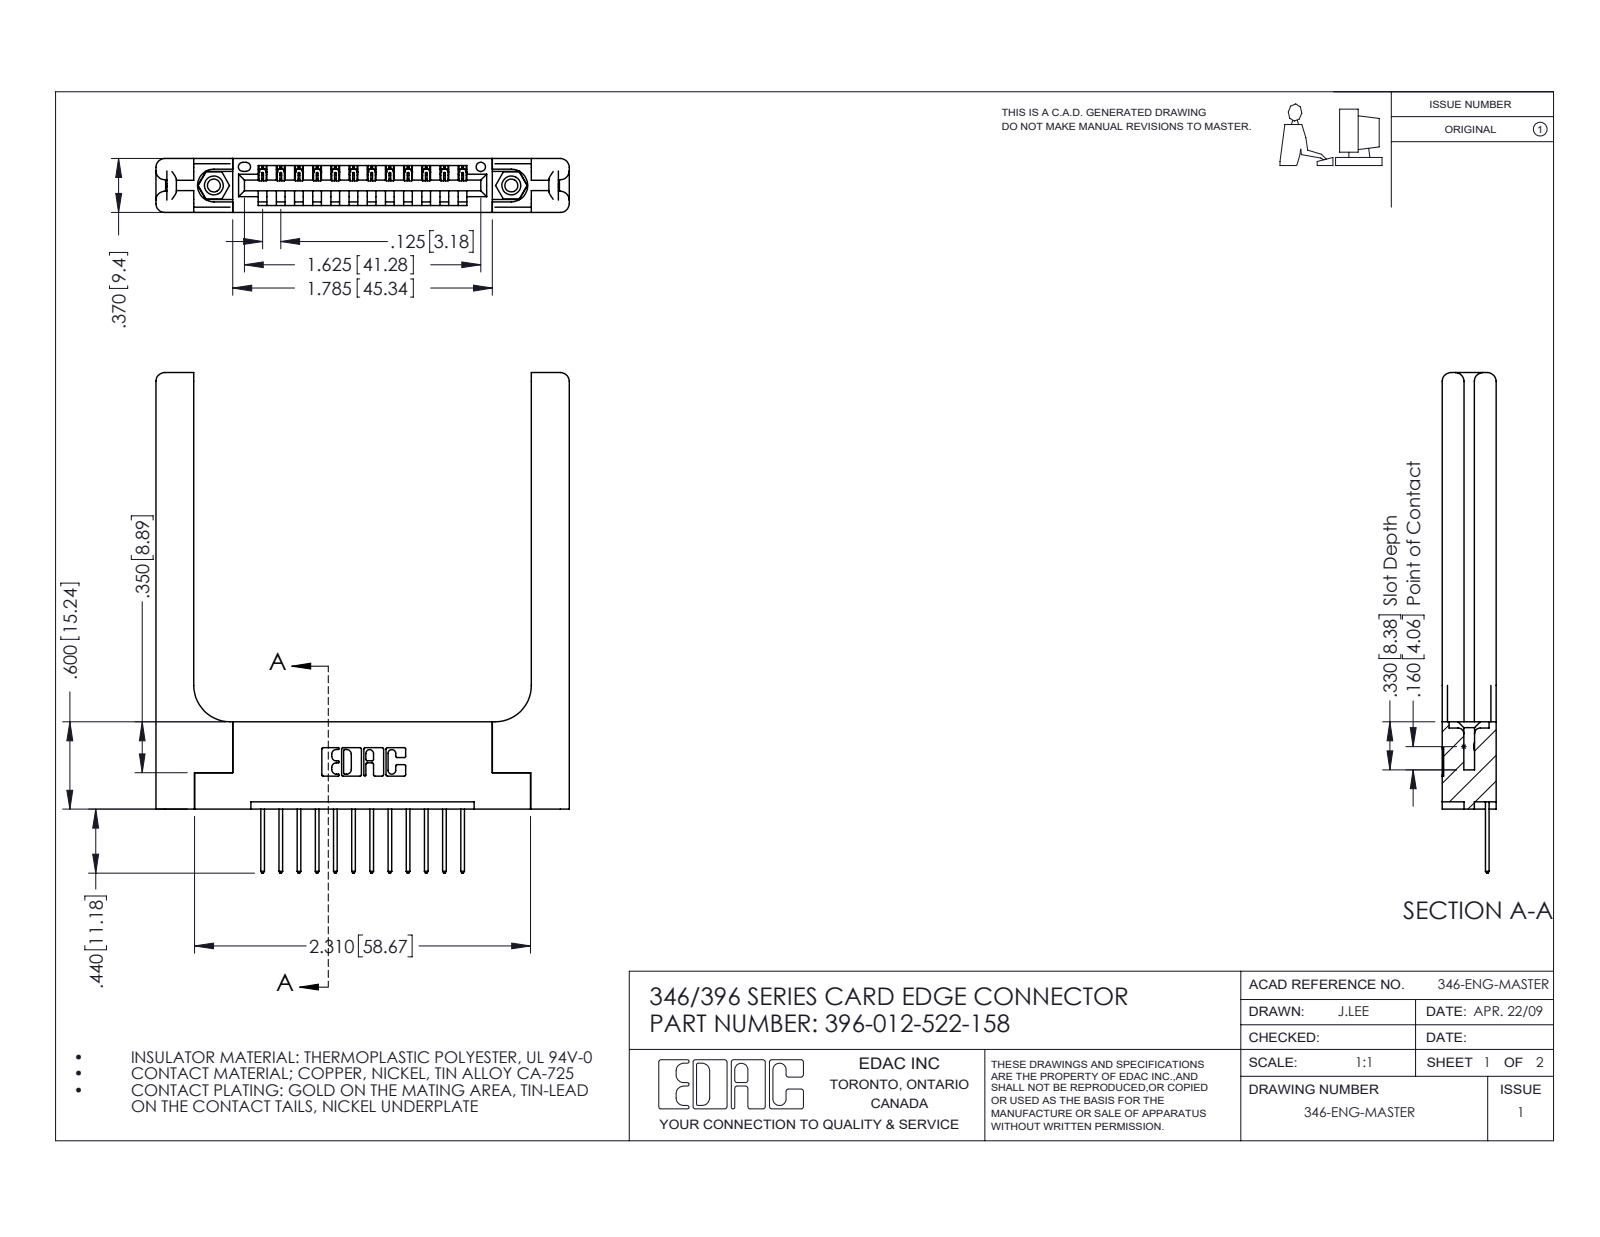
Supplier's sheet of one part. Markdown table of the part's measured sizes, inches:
| quantity | value |
| --- | --- |
| part name | 346 Part_Flush Mounting Lugs - 0.156 Dia-TH; 345-292-001_345-293-122; 396-012-522-158; 346-220-058_345-220-058 (+1 more) |
| STEP written by | SolidWorks 2016 (CONFIG_CONTROL_DESIGN) |
| units | inches |
| bodies | 17 solids, 1074 faces (704 planar, 310 cylindrical, 60 other) |
| overall size | 3.44 × 2.841 × 0.37 |
| volume | 0.868 in³ |
| surface area | 20.56 in² |
| round holes (diameter × count) | 0.089 × 2, 0.125 × 2, 0.156 × 2, 0.064 × 1 |
| round bosses / shafts (diameter × count) | 0.155 × 2 |
| partial cylindrical surfaces (radius × count) | 0.006 × 24, 0.01 × 24, 0.01 × 22, 0.06 × 16, 0.007 × 6, 0.031 × 6, 0.026 × 3, 0.03 × 2 |
| main face-to-face distances | 0.37, 0.15, 0.072, 0.148, 0.048, 0.322, 0.22, 0.25, 0.102, 0.173 |
| hole center spacings | 0.246, 1.839, 2.045 |
